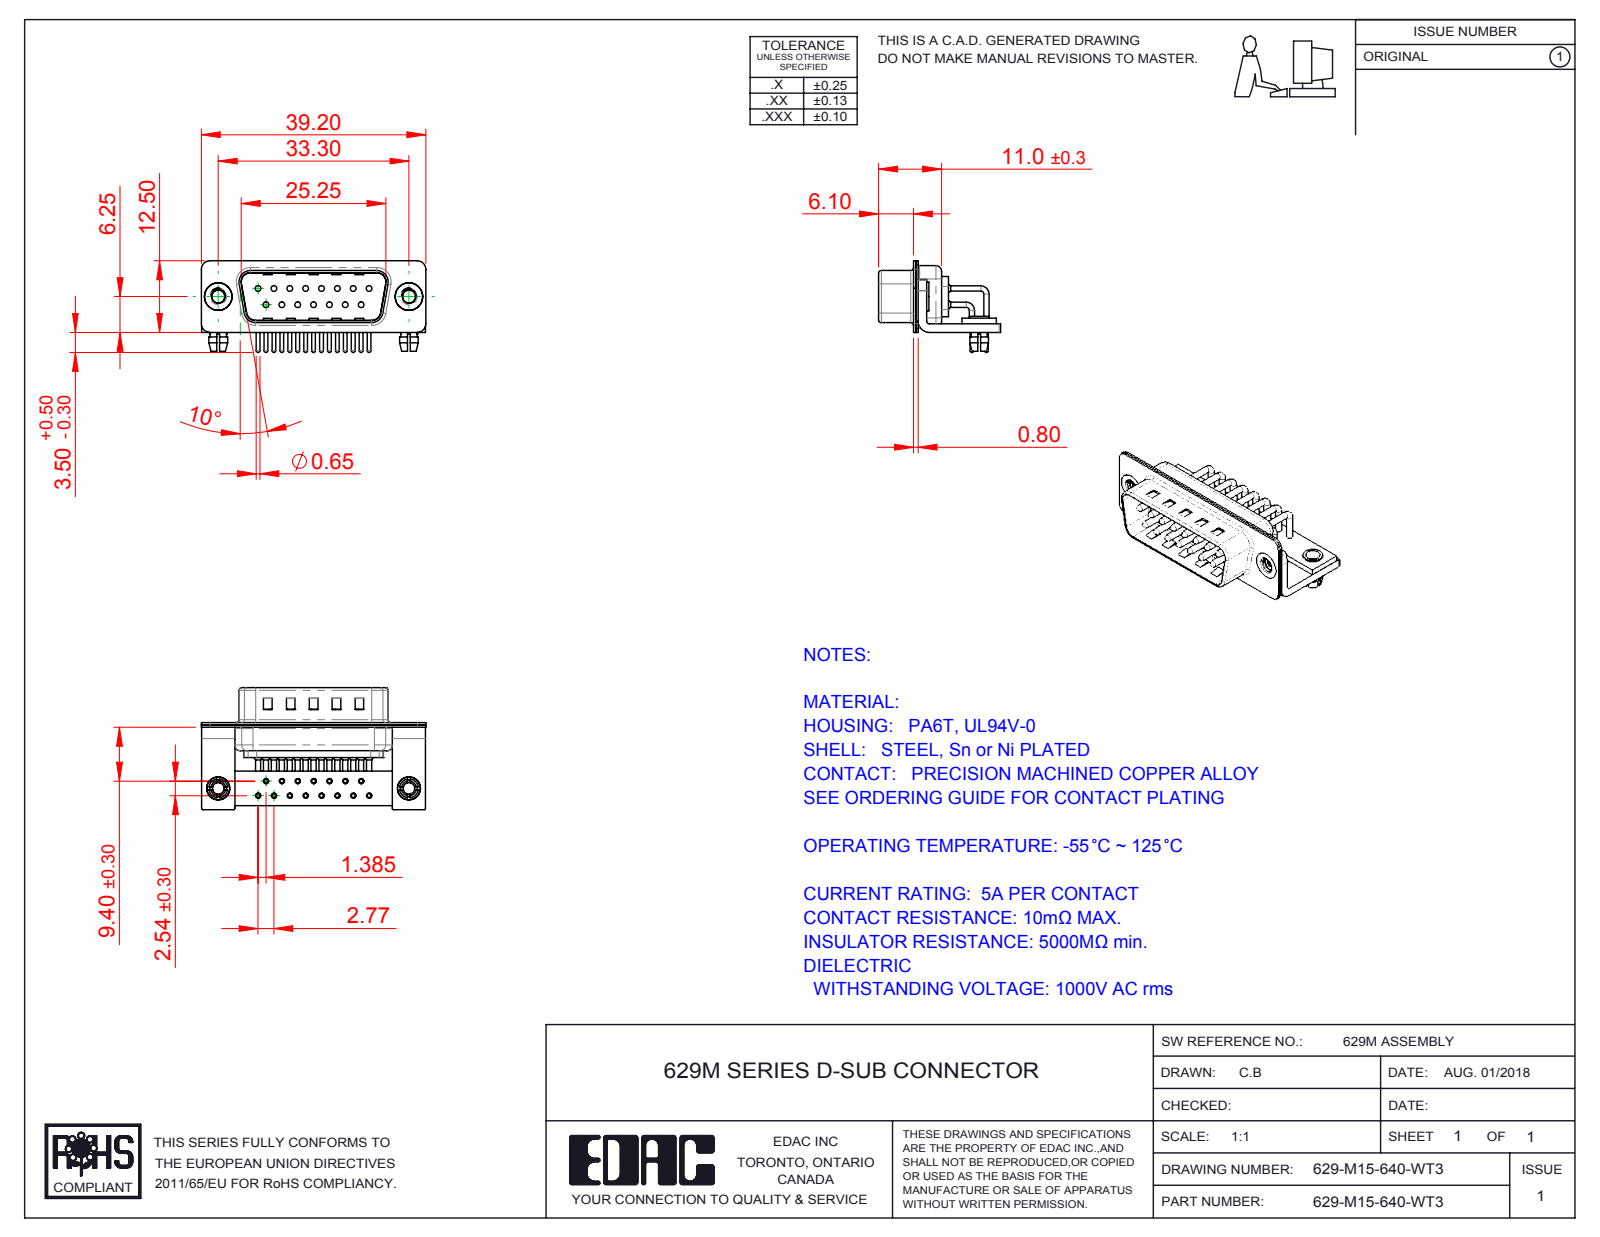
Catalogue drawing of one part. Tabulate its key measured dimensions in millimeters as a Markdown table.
| quantity | value |
| --- | --- |
| part name | 629M Shell Front_15 Contacts; 629M Board Lock; 629M Shell Rear_15 Contacts; 629-M15-640-WT3 (+6 more) |
| STEP written by | SolidWorks 2016 (CONFIG_CONTROL_DESIGN) |
| units | millimeters |
| bodies | 25 solids, 2162 faces (1173 planar, 757 cylindrical, 232 other) |
| overall size | 39.2 × 21.3 × 16 |
| volume | 2 481 mm³ |
| surface area | 6 762 mm² |
| round holes (diameter × count) | 2 × 17, 0.9 × 15, 1 × 15, 1.7 × 15, 2.26 × 2, 2.5 × 2, 3.2 × 2, 4 × 2, 4.8 × 2 |
| round bosses / shafts (diameter × count) | 0.9 × 21, 1.5 × 15, 0.65 × 15, 5 × 2, 4.9 × 2, 4 × 2, 3.4 × 2, 3.3 × 2 |
| partial cylindrical surfaces (radius × count) | 0.25 × 16, 1.5 × 16, 1.01 × 15, 2 × 13, 0.5 × 9, 1.6 × 8, 0.6 × 4, 0.65 × 4 |
| main face-to-face distances | 0.4, 1.5, 0.85, 0.8, 1.25, 10.4, 9.55, 1, 1.9, 9.15 |
| hole center spacings | 2.77, 5.54, 3.16, 8.31, 4.87, 11.08, 2.89, 7.37 |
